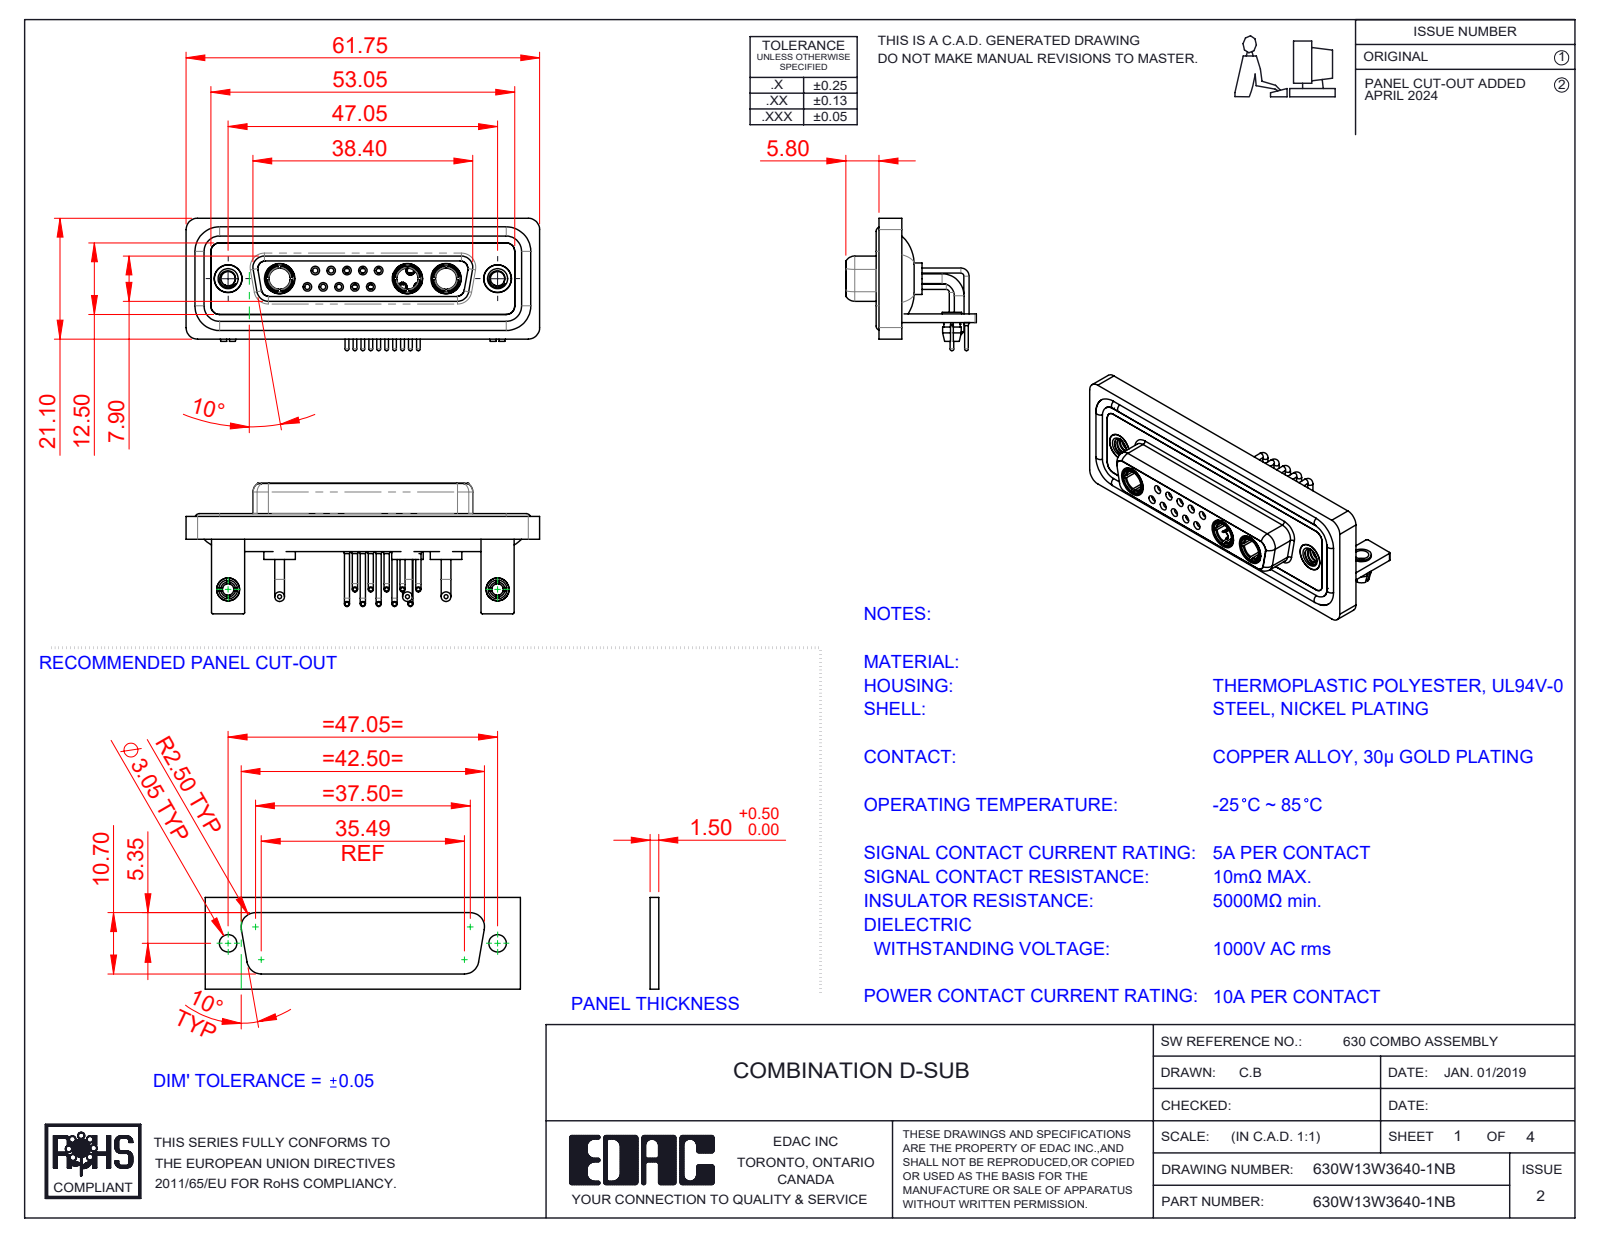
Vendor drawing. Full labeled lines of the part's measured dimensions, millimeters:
Part name (STEP PRODUCT): 630Combo Contact Row 1_50 Contacts; 630Combo Stabilizer Bracket_50 Contacts; 630Combo Waterproof Housing_25 Contacts; 630Combo Threaded Rivet_A (+7 more)
STEP written by: SolidWorks 2023 (CONFIG_CONTROL_DESIGN)
Units: millimetres
Bodies: 27 solids, 1284 faces (410 planar, 547 cylindrical, 327 other)
Overall size (bounding box): 61.75 × 23.12 × 22.8
Volume: 8 693 mm³ · Surface area: 15 093 mm²
Round holes (diameter × count): ⌀2 ×12, ⌀0.9 ×10, ⌀1.1 ×10, ⌀1.5 ×10, ⌀1.6 ×5, ⌀1.7 ×5, ⌀4.85 ×5, ⌀2.5 ×4, ⌀3.7 ×3, ⌀5.3 ×3, ⌀3.2 ×2, ⌀4 ×2
Round bosses / shafts (diameter × count): ⌀0.9 ×15, ⌀1.6 ×12, ⌀0.65 ×10, ⌀1.7 ×6, ⌀2 ×5, ⌀1.5 ×5, ⌀5.5 ×3, ⌀5.2 ×3
Partial cylindrical surfaces — rounded edges, fillets, slot ends (radius × count): R2 ×19, R1.5 ×18, R0.25 ×16, R1.35 ×8, R1.6 ×8, R0.5 ×5, R0.6 ×4, R0.65 ×4
Main face-to-face distances: 0.4, 1.8, 2.9, 1.5, 3.7, 4.1, 1.1, 1.4, 1.6, 3.1
Hole centre spacings: 3.16, 2.77, 5.54, 5.04, 8.31, 5.03, 7.49, 11.08
